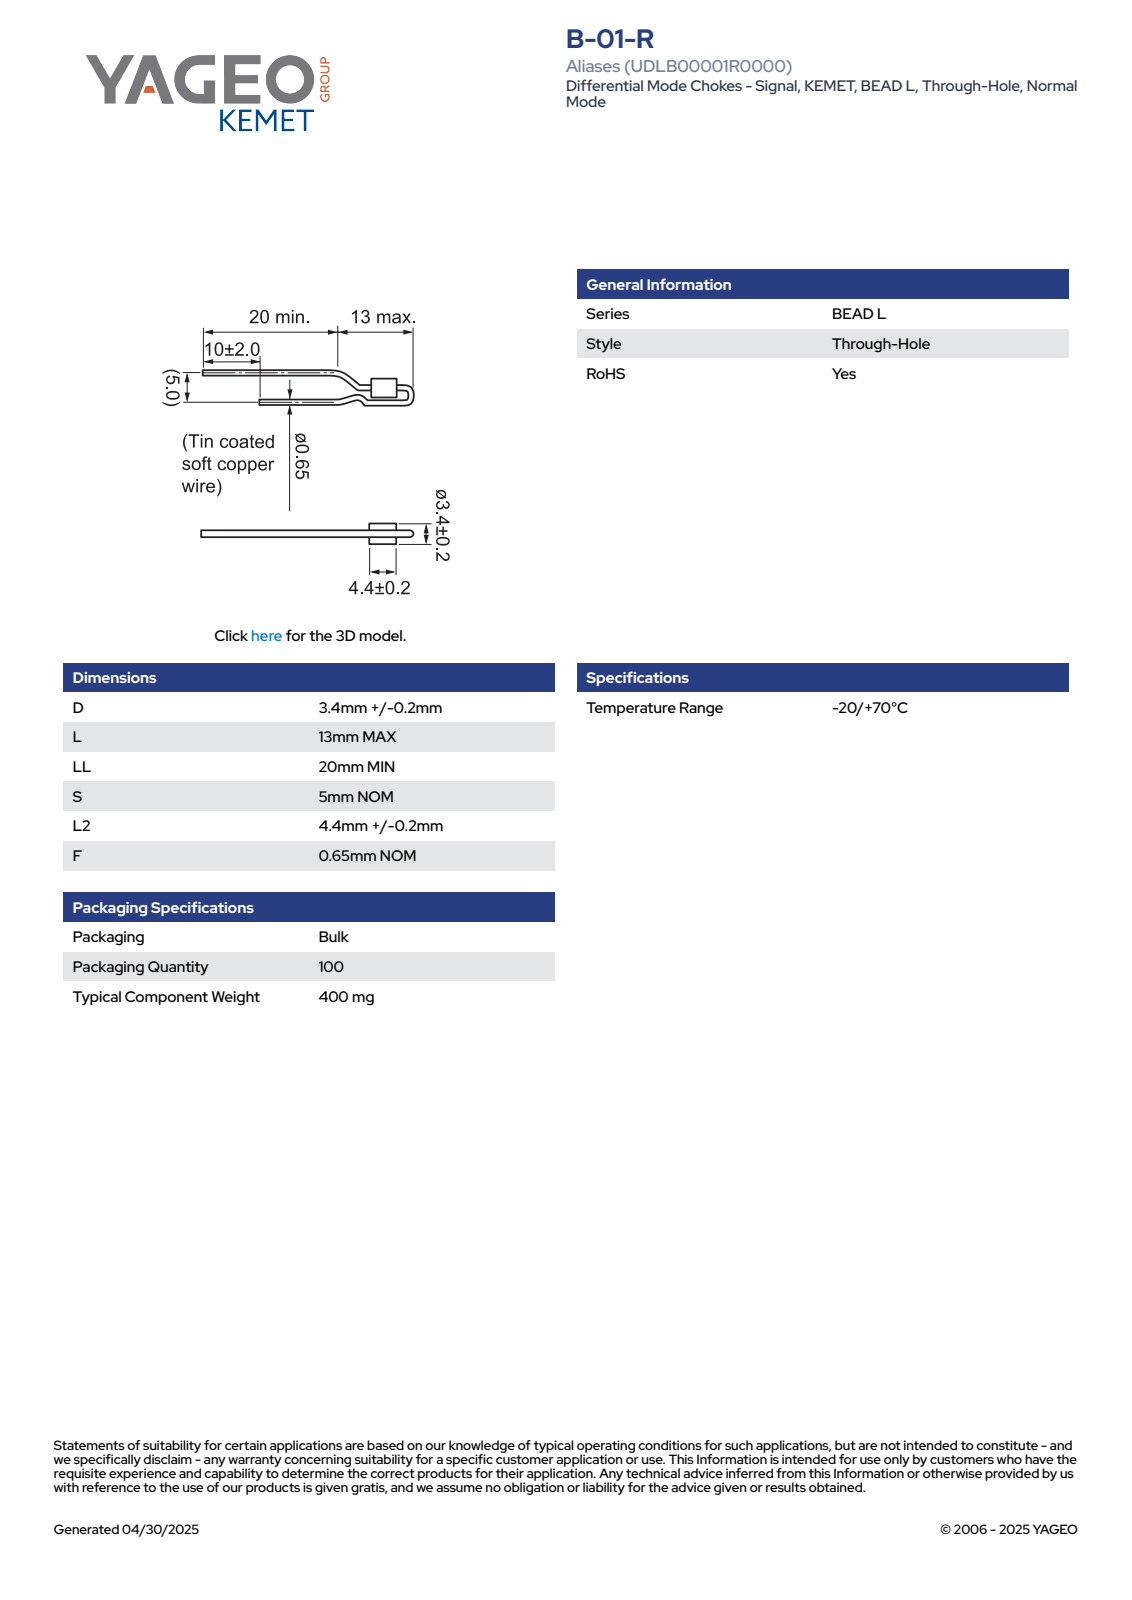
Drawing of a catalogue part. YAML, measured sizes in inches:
part_name: "IL_B01R_D3.6L13L24.6S5LL20LL210"
step_written_by: "SolidWorks 2014 (AUTOMOTIVE_DESIGN)"
units: inches
bodies: {solids: 1, faces: 100, planar: 26, cylindrical: 29, other: 45}
overall_size: [1.299, 0.222, 0.142]
volume: 0.004
surface_area: 0.277
round_bosses_or_shafts:
  - {diameter: 0.026, count: 7}
  - {diameter: 0.142, count: 1}
partial_cylinders:
  - {radius: 0.071, count: 1}
face_to_face_distances: [0.181, 0.472, 0.961, 1.142, 0.488, 0.669]
